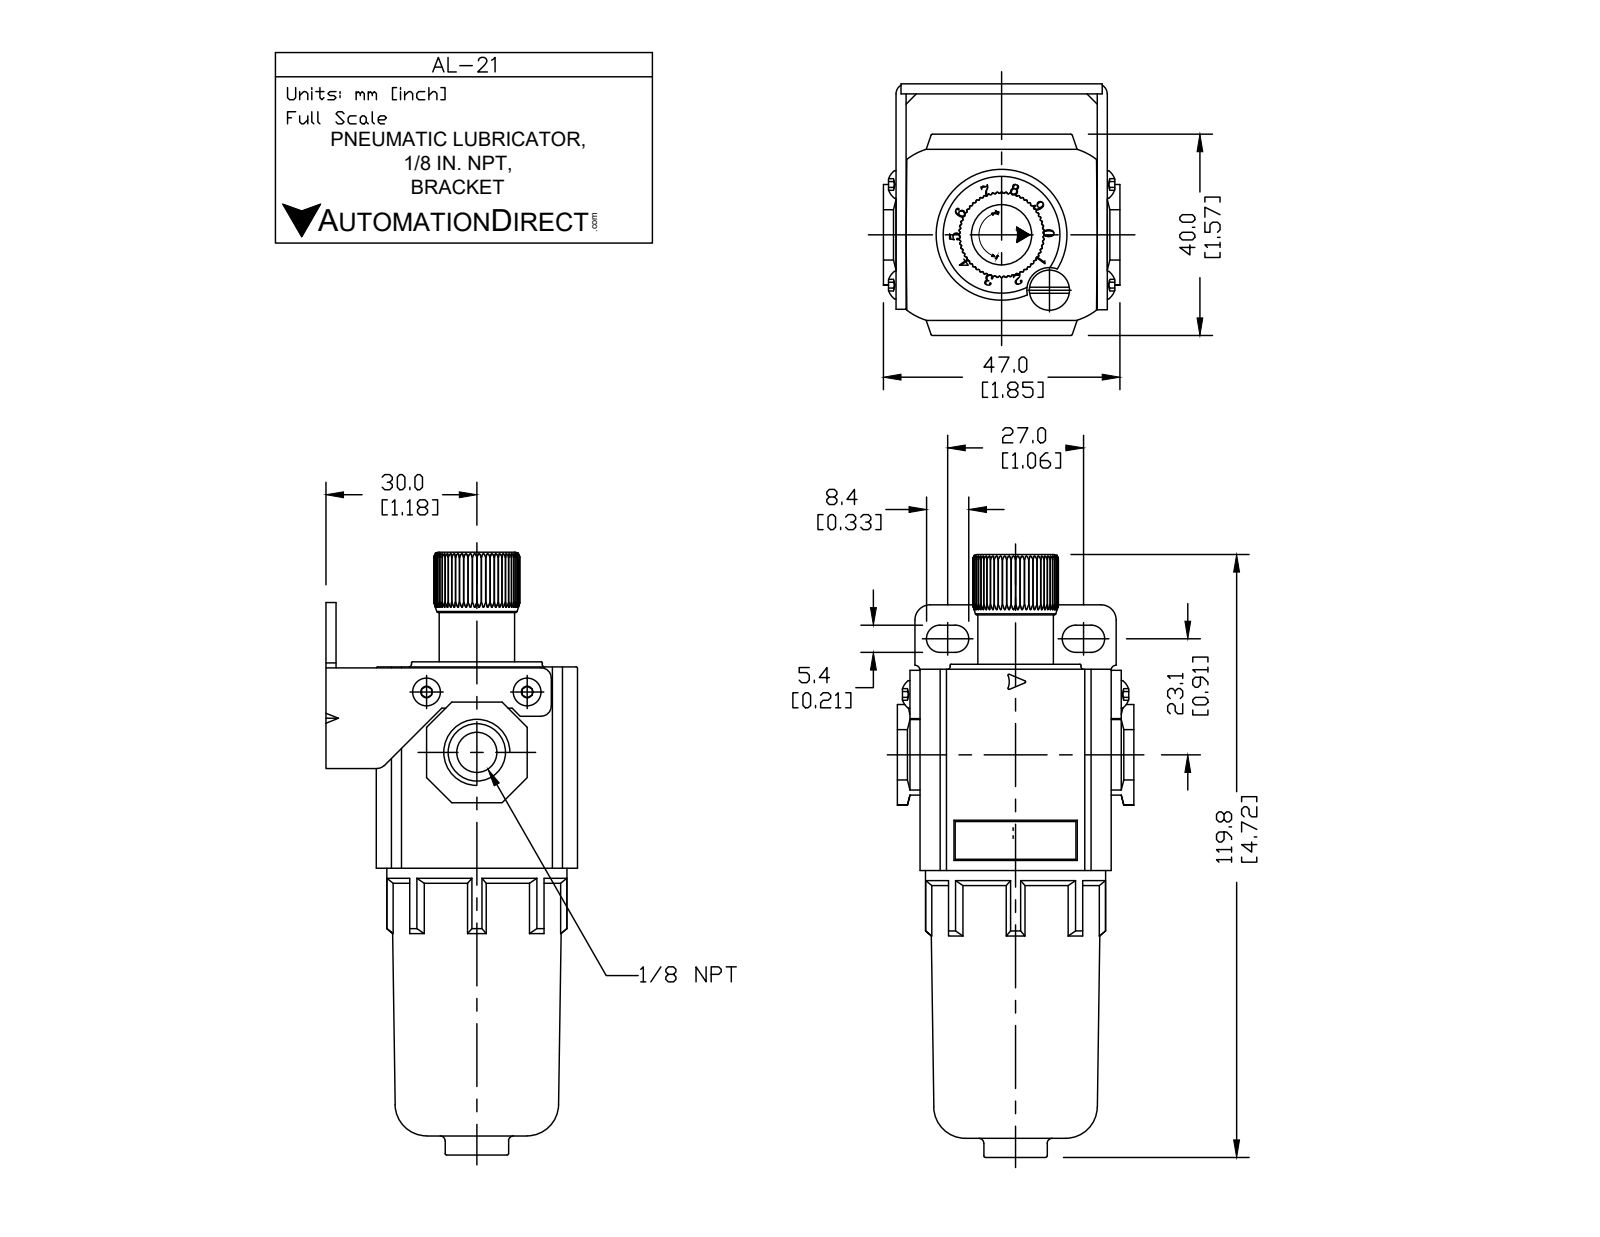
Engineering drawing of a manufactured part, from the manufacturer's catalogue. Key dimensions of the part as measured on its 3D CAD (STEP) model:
Part name (STEP PRODUCT): AL-21
STEP written by: SolidWorks 2015 (CONFIG_CONTROL_DESIGN)
Units: millimetres
Bodies: 7 solids, 508 faces (299 planar, 97 cylindrical, 112 other)
Overall size (bounding box): 118.8 × 50 × 47
Volume: 92 907 mm³ · Surface area: 28 626 mm²
Round holes (diameter × count): ⌀3.4 ×2, ⌀8.43 ×1, ⌀24.8 ×1, ⌀25 ×1
Round bosses / shafts (diameter × count): ⌀36 ×1, ⌀34 ×1, ⌀26 ×1, ⌀15 ×1, ⌀12.6 ×1
Partial cylindrical surfaces — rounded edges, fillets, slot ends (radius × count): R2 ×5, R0.3 ×4, R2.7 ×4, R12 ×4, R3 ×2, R4 ×2, R8.5 ×1, R16.9 ×1
Main face-to-face distances: 40, 2, 38, 10, 50, 8, 48, 4.5, 42, 2.5
Hole centre spacings: 15.62, 20
